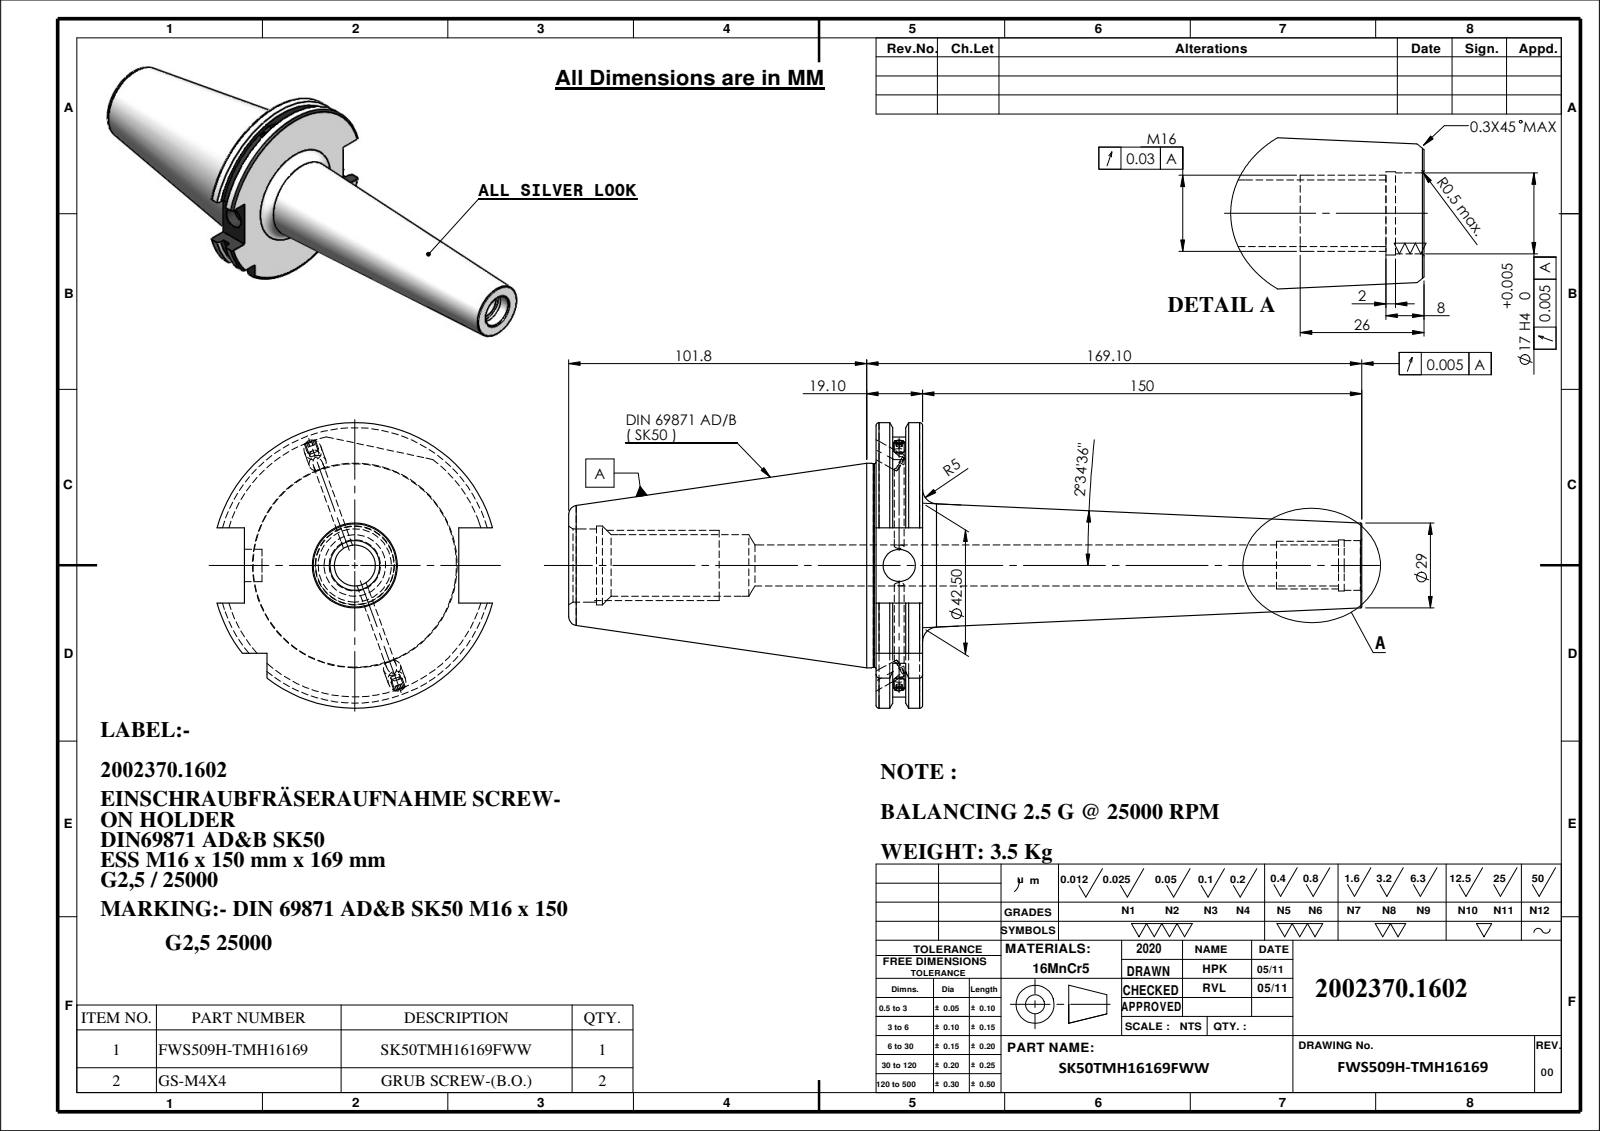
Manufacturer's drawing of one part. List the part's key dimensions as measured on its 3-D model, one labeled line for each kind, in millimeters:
Part name (STEP PRODUCT): M4X4_DIN 913 - M4 x 4-N; SK50TMH16169FWW; 91506-ES7M16150
STEP written by: SolidWorks 2018 (AUTOMOTIVE_DESIGN)
Units: millimetres
Bodies: 3 solids, 138 faces (43 planar, 47 cylindrical, 48 other)
Overall size (bounding box): 270.85 × 97.5 × 94.05
Volume: 458 285 mm³ · Surface area: 66 606 mm²
Round holes (diameter × count): ⌀6 ×2, ⌀3.3 ×1, ⌀11 ×1, ⌀14 ×1, ⌀17 ×1, ⌀17.5 ×1, ⌀21 ×1, ⌀25 ×1, ⌀27 ×1
Round bosses / shafts (diameter × count): ⌀4 ×2, ⌀69.85 ×1, ⌀69.45 ×1
Partial cylindrical surfaces — rounded edges, fillets, slot ends (radius × count): R44.9 ×1, R48.75 ×1
Main face-to-face distances: 15.9, 5.65, 10.25, 10.14, 4.49, 5.76, 104.95, 110.6, 115.09, 120.85
